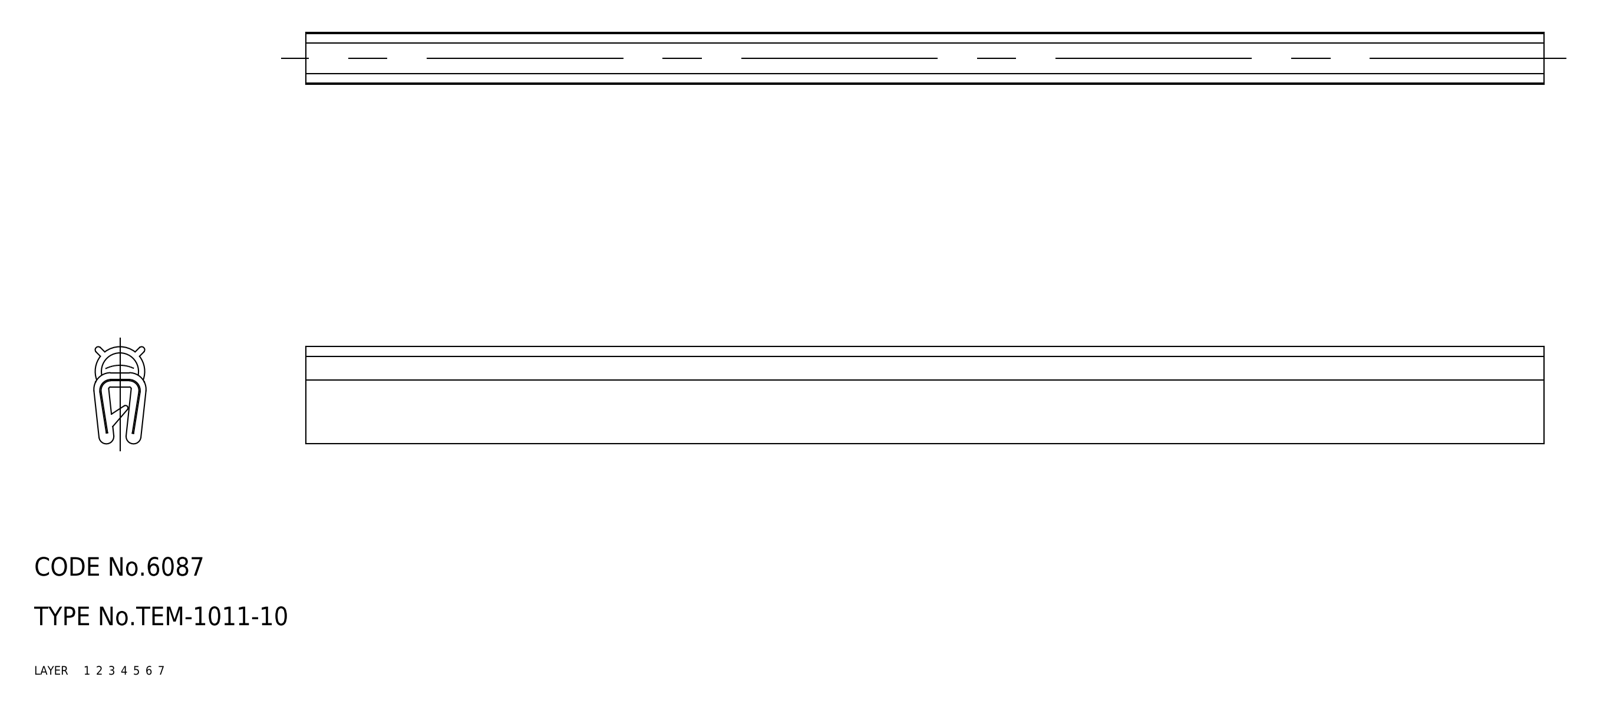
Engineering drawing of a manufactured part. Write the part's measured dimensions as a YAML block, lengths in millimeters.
part_name: "rubber foam; gasket; center core; TEM_1011_10_30360_36"
step_written_by: "CADfix (AUTOMOTIVE_DESIGN)"
units: millimeters
bodies: {solids: 3, faces: 61, planar: 0, cylindrical: 0, other: 61}
overall_size: [200, 15.7, 8.43]
volume: 15798
surface_area: 36514
